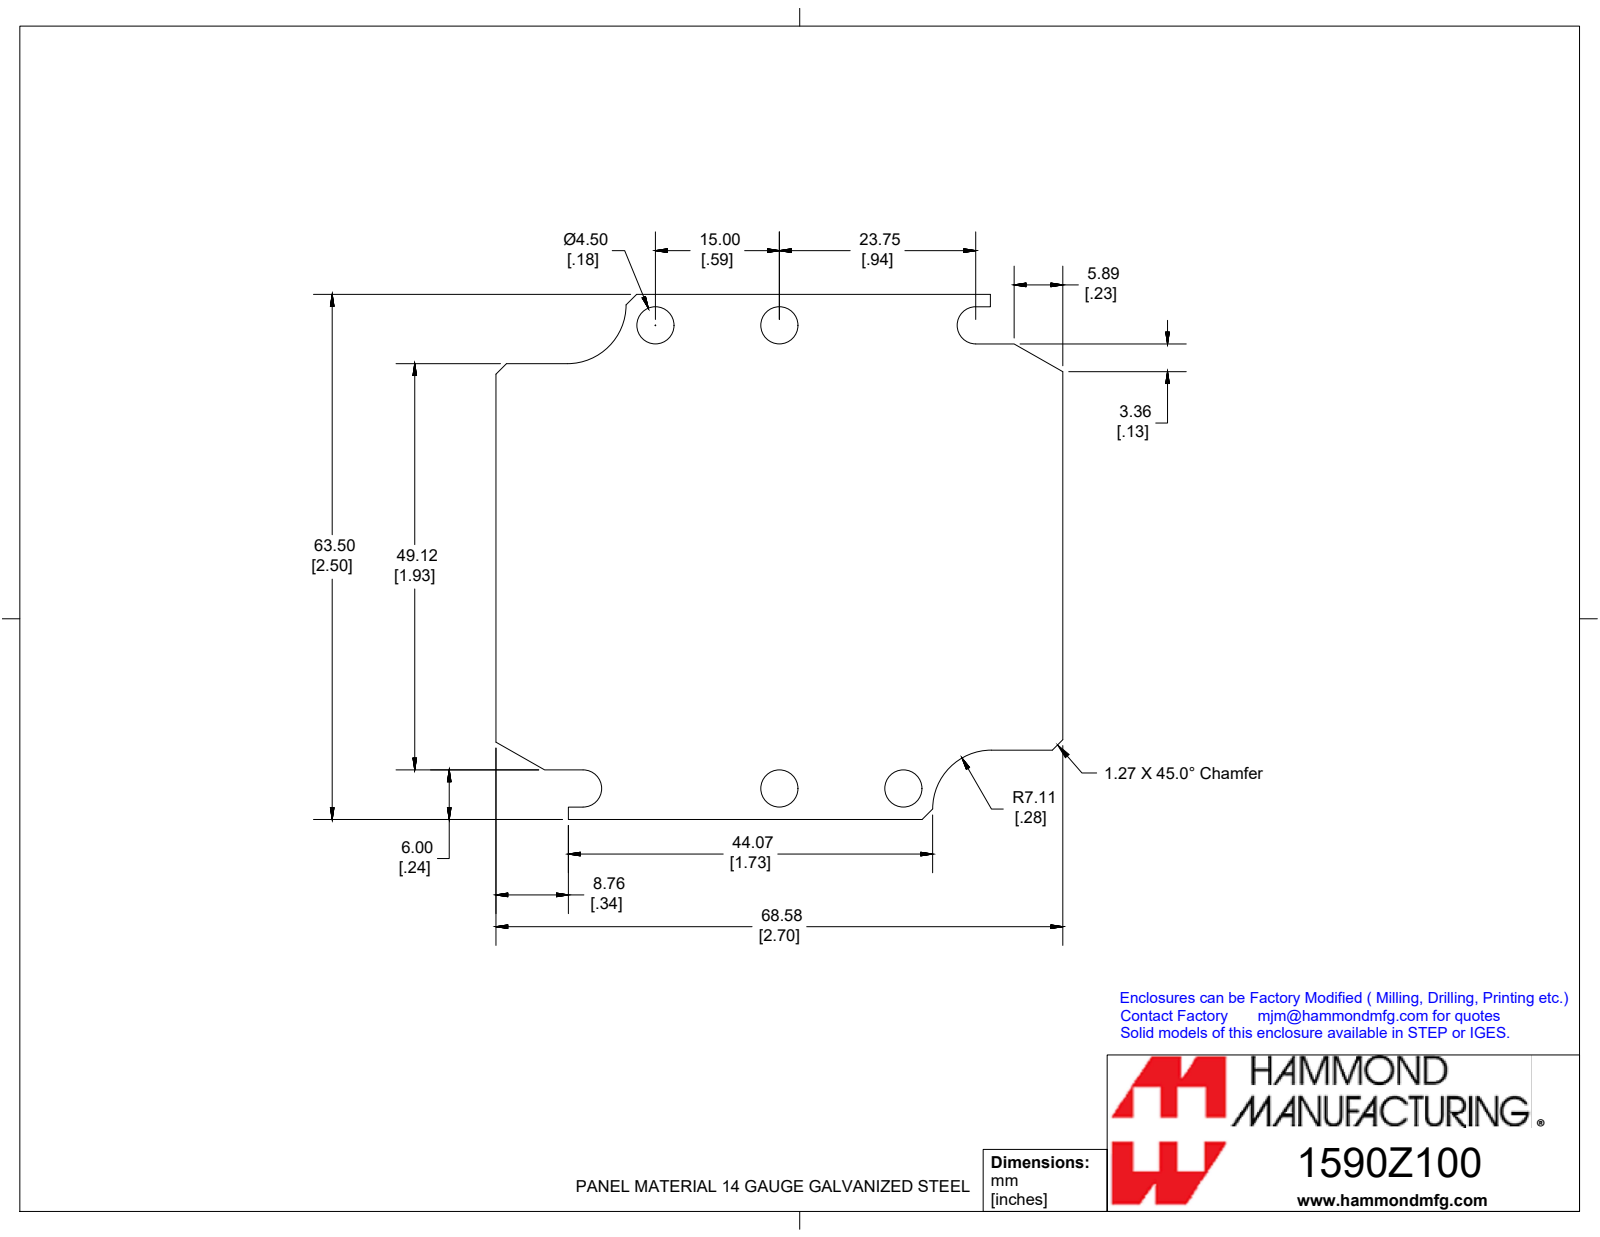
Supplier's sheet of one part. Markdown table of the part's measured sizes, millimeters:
| quantity | value |
| --- | --- |
| part name | 1590Z100PL |
| STEP written by | SolidWorks 2019 (CONFIG_CONTROL_DESIGN) |
| units | millimeters |
| bodies | 1 solid, 28 faces (20 planar, 8 cylindrical, 0 other) |
| overall size | 68.6 × 63.5 × 1.6 |
| volume | 6 280 mm³ |
| surface area | 8 290 mm² |
| round holes (diameter × count) | 4.5 × 4 |
| partial cylindrical surfaces (radius × count) | 2.3 × 2, 7.1 × 2 |
| main face-to-face distances | 1.6, 68.6, 63.5, 8.4, 55.1, 6, 57.5, 2.4, 49.1, 46.7 |
| hole center spacings | 15, 58, 56, 63.5 |
